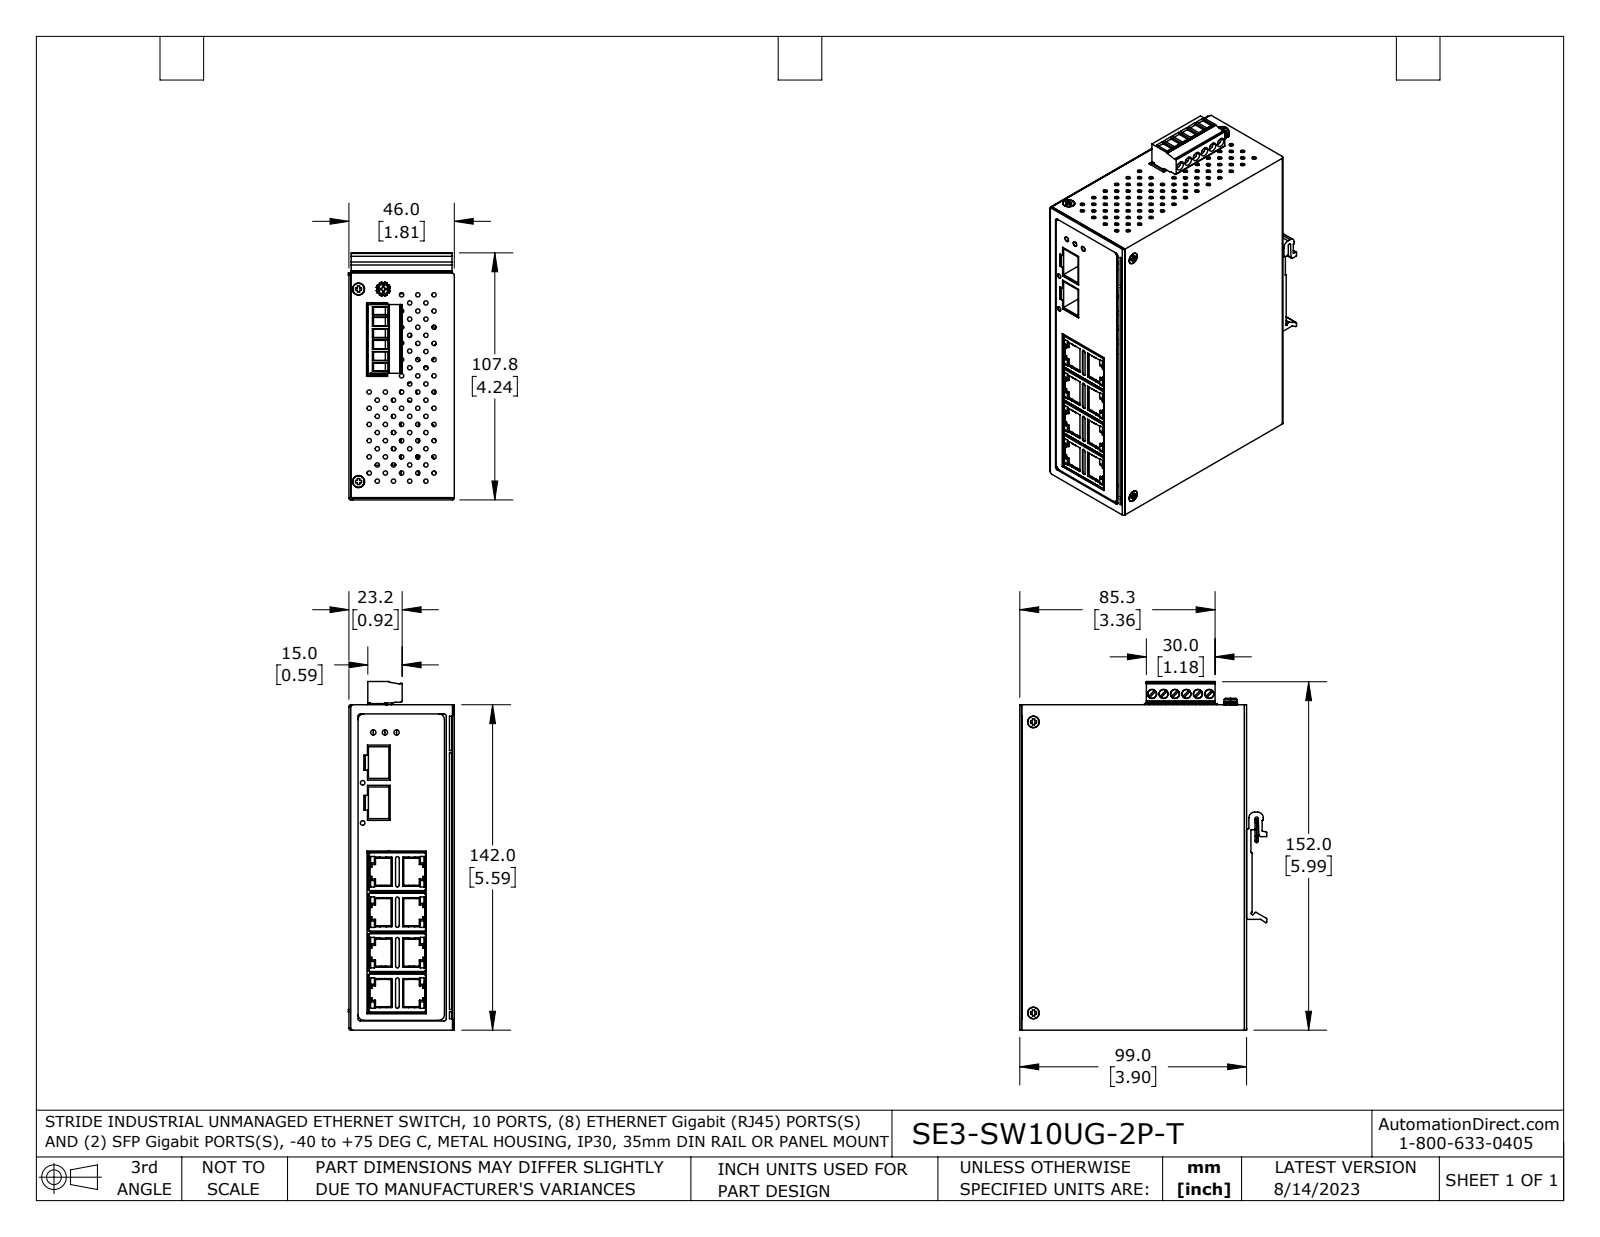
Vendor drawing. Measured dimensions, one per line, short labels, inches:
name: LEONTON_EG2-0800_3D sr1 solid but 16 bad faces1 extTB1ac coord pre CASE MOD for EG2-1002sfp 1aCd cmb1Cc 46MM CASE ONLY mm COMBaB Modn1 coord fxt
written by: SolidWorks 2021 (AUTOMOTIVE_DESIGN)
unit: in
bodies: 33 solids, 3512 faces (1754 planar, 1333 cylindrical, 425 other)
size: 5.99 × 4.244 × 1.821
volume: 9.242 in³; area: 221.4 in²
holes: 153× ⌀0.075, 42× ⌀0.094, 9× ⌀0.157, 8× ⌀0.098, 3× ⌀0.091, 3× ⌀0.096, 3× ⌀0.097, 3× ⌀0.118, 2× ⌀0.079, 2× ⌀0.197, 2× ⌀0.209
bosses: 10× ⌀0.197, 10× ⌀0.094, 8× ⌀0.161, 6× ⌀0.149, 6× ⌀0.055, 6× ⌀0.035, 3× ⌀0.165, 3× ⌀0.157
rounds: 84× R0.006, 81× R0.004, 39× R0.008, 30× R0.016, 24× R0.01, 22× R0.012, 22× R0.039, 18× R0.016
face distances: 0.031, 0.039, 1.74, 1.78, 1.772, 1.811, 5.559, 0.02, 0.157, 5.591
hole spacings: 0.278, 0.197, 0.394, 0.44, 0.557, 0.622, 0.709, 0.44
